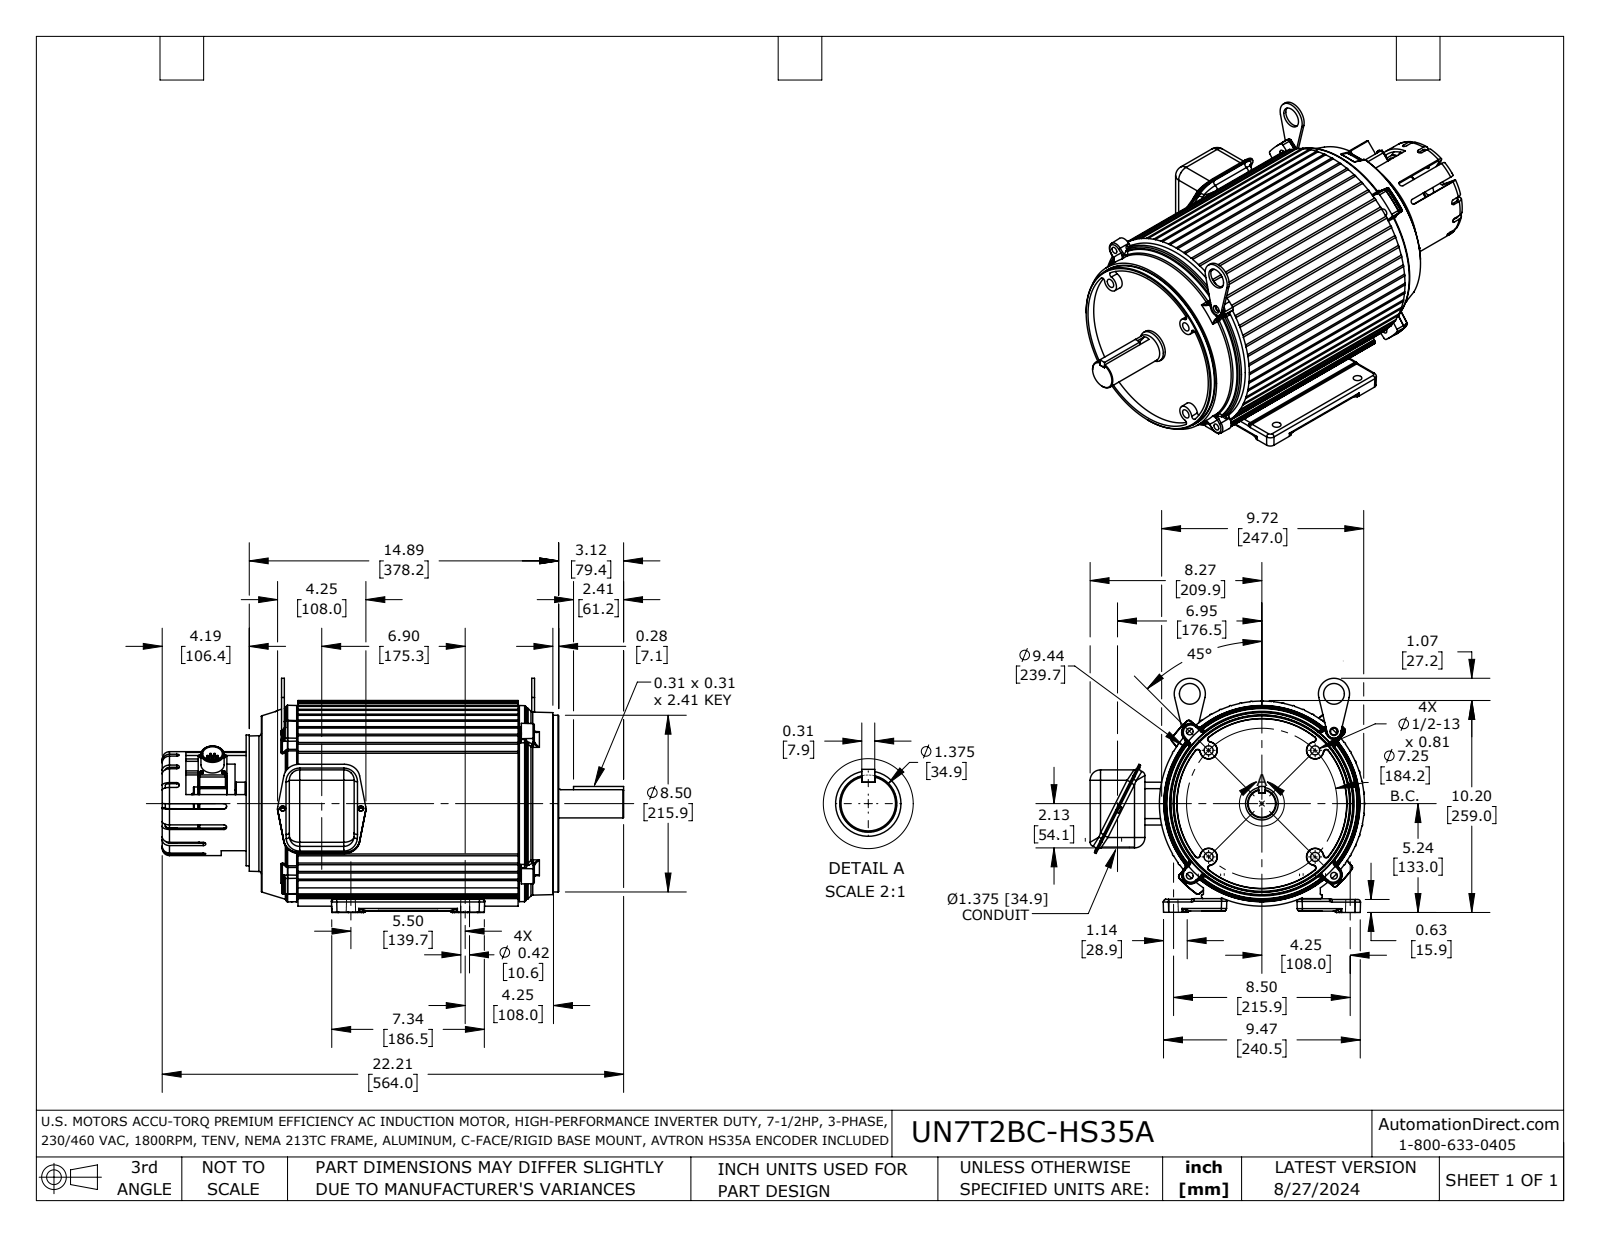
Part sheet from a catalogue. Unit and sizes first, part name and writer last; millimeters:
Units: millimetres
Overall size (bounding box): 564 × 335.9 × 287.7
Round holes (diameter × count): ⌀10.2 ×6, ⌀3 ×4, ⌀5.1 ×4, ⌀8 ×4, ⌀8.3 ×4, ⌀11.1 ×4, ⌀3.5 ×3, ⌀25.4 ×3, ⌀2.7 ×2, ⌀5.8 ×2, ⌀7.1 ×2, ⌀9.9 ×2
Round bosses / shafts (diameter × count): ⌀1.8 ×8, ⌀3 ×4, ⌀3.8 ×3, ⌀8.2 ×2, ⌀4.4 ×2, ⌀4.4 ×2, ⌀1.8 ×2, ⌀250.6 ×1
Partial cylindrical surfaces — rounded edges, fillets, slot ends (radius × count): R3.2 ×170, R1.6 ×68, R1.5 ×60, R2.5 ×58, R6.4 ×22, R0.8 ×18, R12.7 ×18, R3 ×16
Main face-to-face distances: 345.8, 50.3, 396.1, 85.2, 27.4, 22.9, 368.6, 48.3, 20.9, 2
Hole centre spacings: 53.4, 68.3, 98.3, 110.6, 118.5, 127.5, 145.3, 154.9
Volume: 18 370 000 mm³ · Surface area: 867 100 mm²
Bodies: 21 solids, 2789 faces (686 planar, 881 cylindrical, 1222 other)
Part name (STEP PRODUCT): UN7T2BC-HS35A
STEP written by: SolidWorks 2021 (AUTOMOTIVE_DESIGN)
